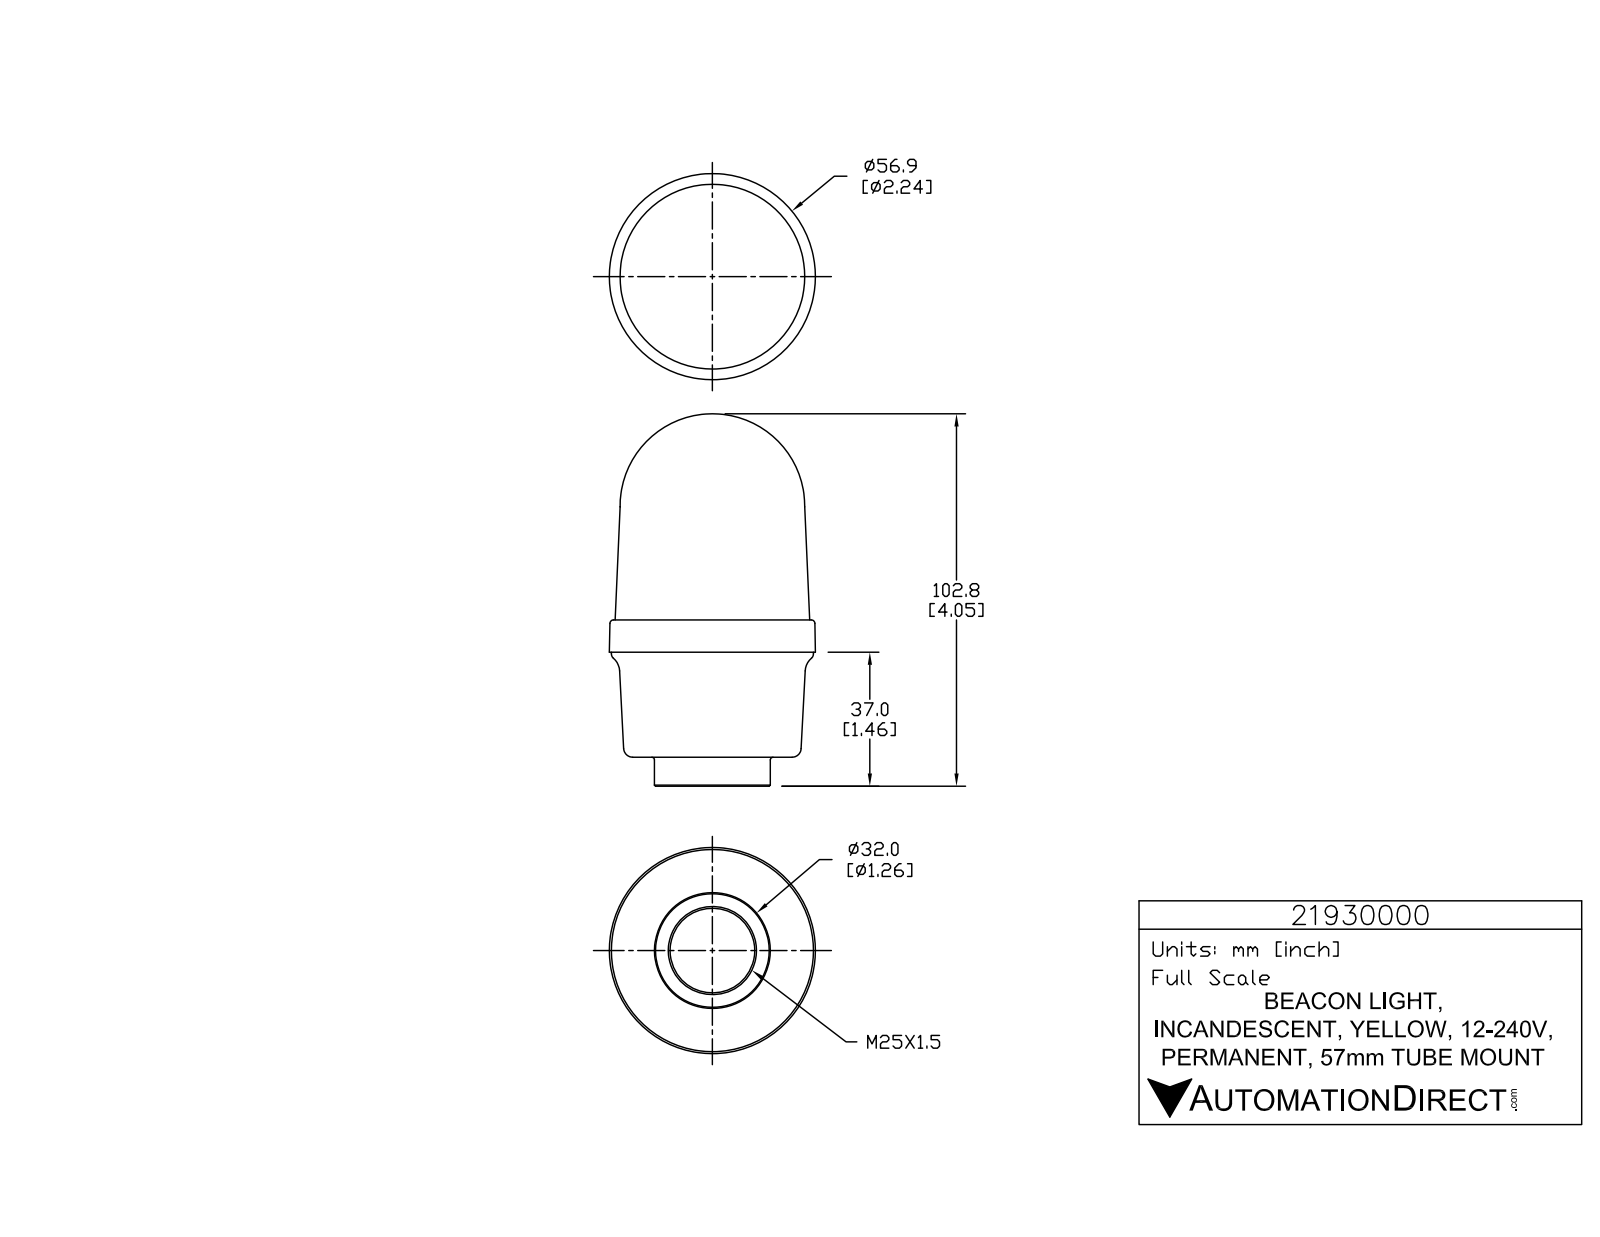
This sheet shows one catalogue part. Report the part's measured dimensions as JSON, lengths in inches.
{"part_name": "21930000", "step_written_by": "SolidWorks 2015 (AUTOMOTIVE_DESIGN)", "units": "inches", "bodies": {"solids": 1, "faces": 764, "planar": 524, "cylindrical": 145, "other": 95}, "overall_size": [4.047, 2.24, 2.24], "volume_in3": 11.36, "surface_area_in2": 29.4, "round_holes": [[0.039, 3], [0.92, 1]], "round_bosses_or_shafts": [[0.226, 3], [0.056, 3], [2.197, 1], [1.26, 1]], "partial_cylinders_radius": [[0.008, 6], [0.008, 6], [0.008, 6], [0.131, 6], [0.004, 3], [0.005, 3], [0.007, 3], [0.008, 3]], "face_to_face_distances": [0.315, 1.142, 1.457, 0.35, 1.492, 1.807, 0.418, 0.768, 1.91, 2.225]}
